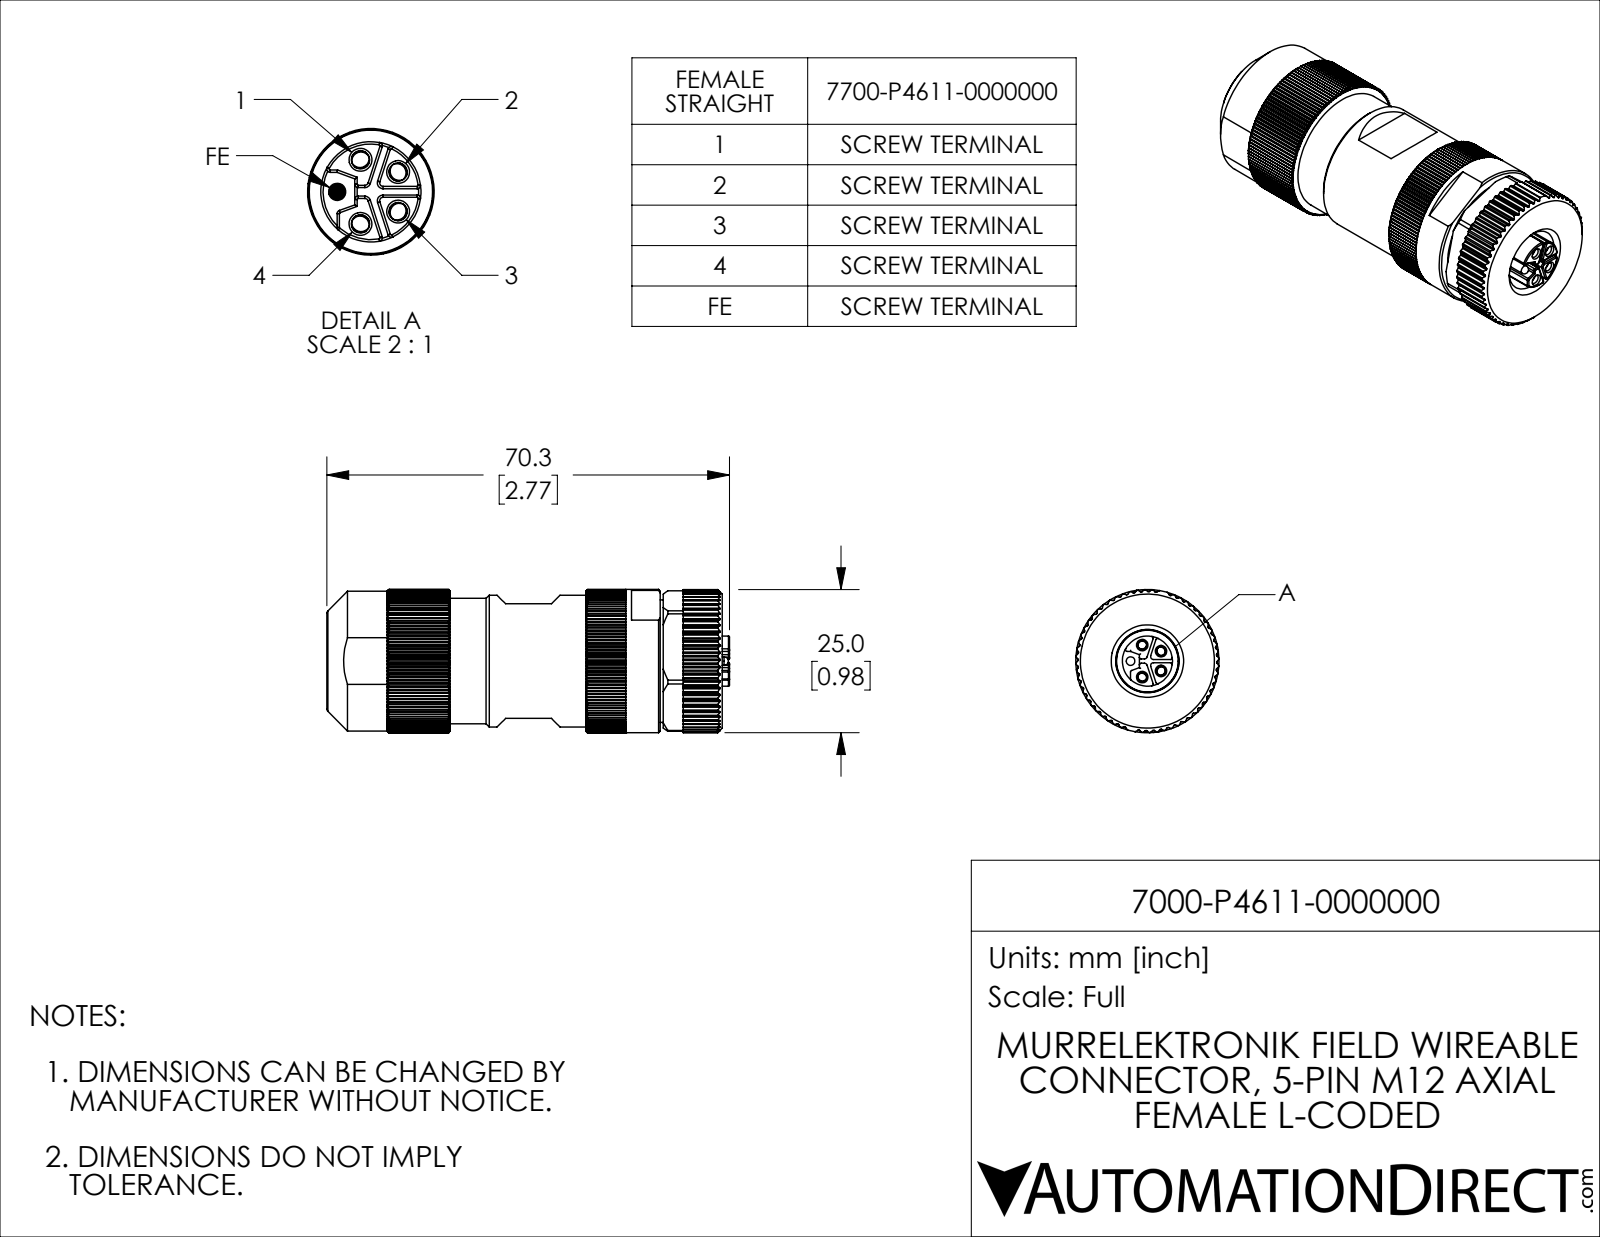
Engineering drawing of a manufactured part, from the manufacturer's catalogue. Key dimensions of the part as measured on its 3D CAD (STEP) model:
Part name (STEP PRODUCT): 7000-P4611-0000000
STEP written by: SolidWorks 2021 (CONFIG_CONTROL_DESIGN)
Units: inches
Bodies: 1 solid, 1418 faces (878 planar, 409 cylindrical, 131 other)
Overall size (bounding box): 2.768 × 0.984 × 0.984
Volume: 1.807 in³ · Surface area: 12.8 in²
Round holes (diameter × count): ⌀0.063 ×4, ⌀0.091 ×4, ⌀0.429 ×1, ⌀0.435 ×1, ⌀0.476 ×1, ⌀0.52 ×1
Round bosses / shafts (diameter × count): ⌀0.087 ×4, ⌀0.984 ×1, ⌀0.906 ×1, ⌀0.863 ×1, ⌀0.843 ×1, ⌀0.344 ×1, ⌀0.059 ×1
Partial cylindrical surfaces — rounded edges, fillets, slot ends (radius × count): R0.008 ×132, R0.012 ×11, R0.031 ×8, R0.043 ×8, R0.02 ×6, R0.006 ×4, R0.48 ×1
Main face-to-face distances: 2.665, 0.866, 0.759, 0.906, 2.239, 0.426, 0.787, 0.794, 1.445, 1.871
Hole centre spacings: 0.116, 0.136, 0.22
